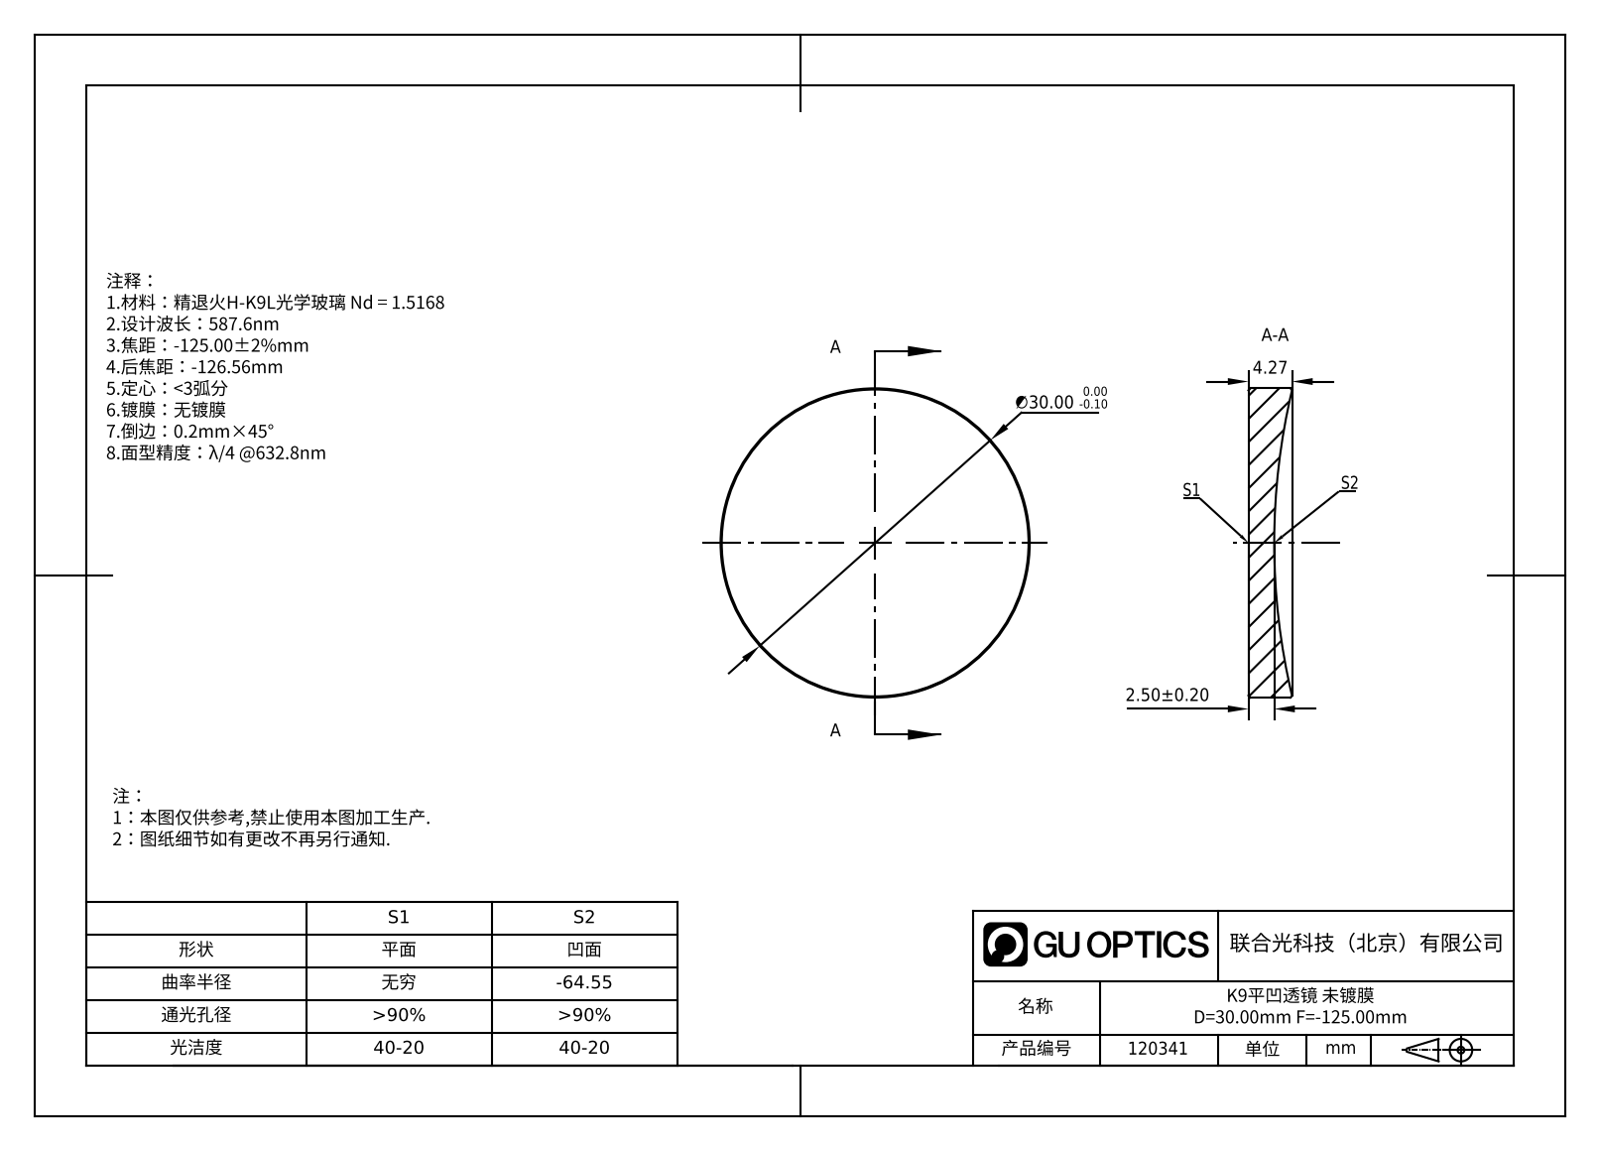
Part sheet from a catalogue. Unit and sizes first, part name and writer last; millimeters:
Units: millimetres
Overall size (bounding box): 30 × 30 × 4.23
Round bosses / shafts (diameter × count): ⌀30 ×1
Volume: 2 387 mm³ · Surface area: 1 802 mm²
Bodies: 1 solid, 9 faces (1 planar, 2 cylindrical, 6 other)
Part name (STEP PRODUCT): GL13-030-125
STEP written by: SolidWorks 2022 (AUTOMOTIVE_DESIGN)
